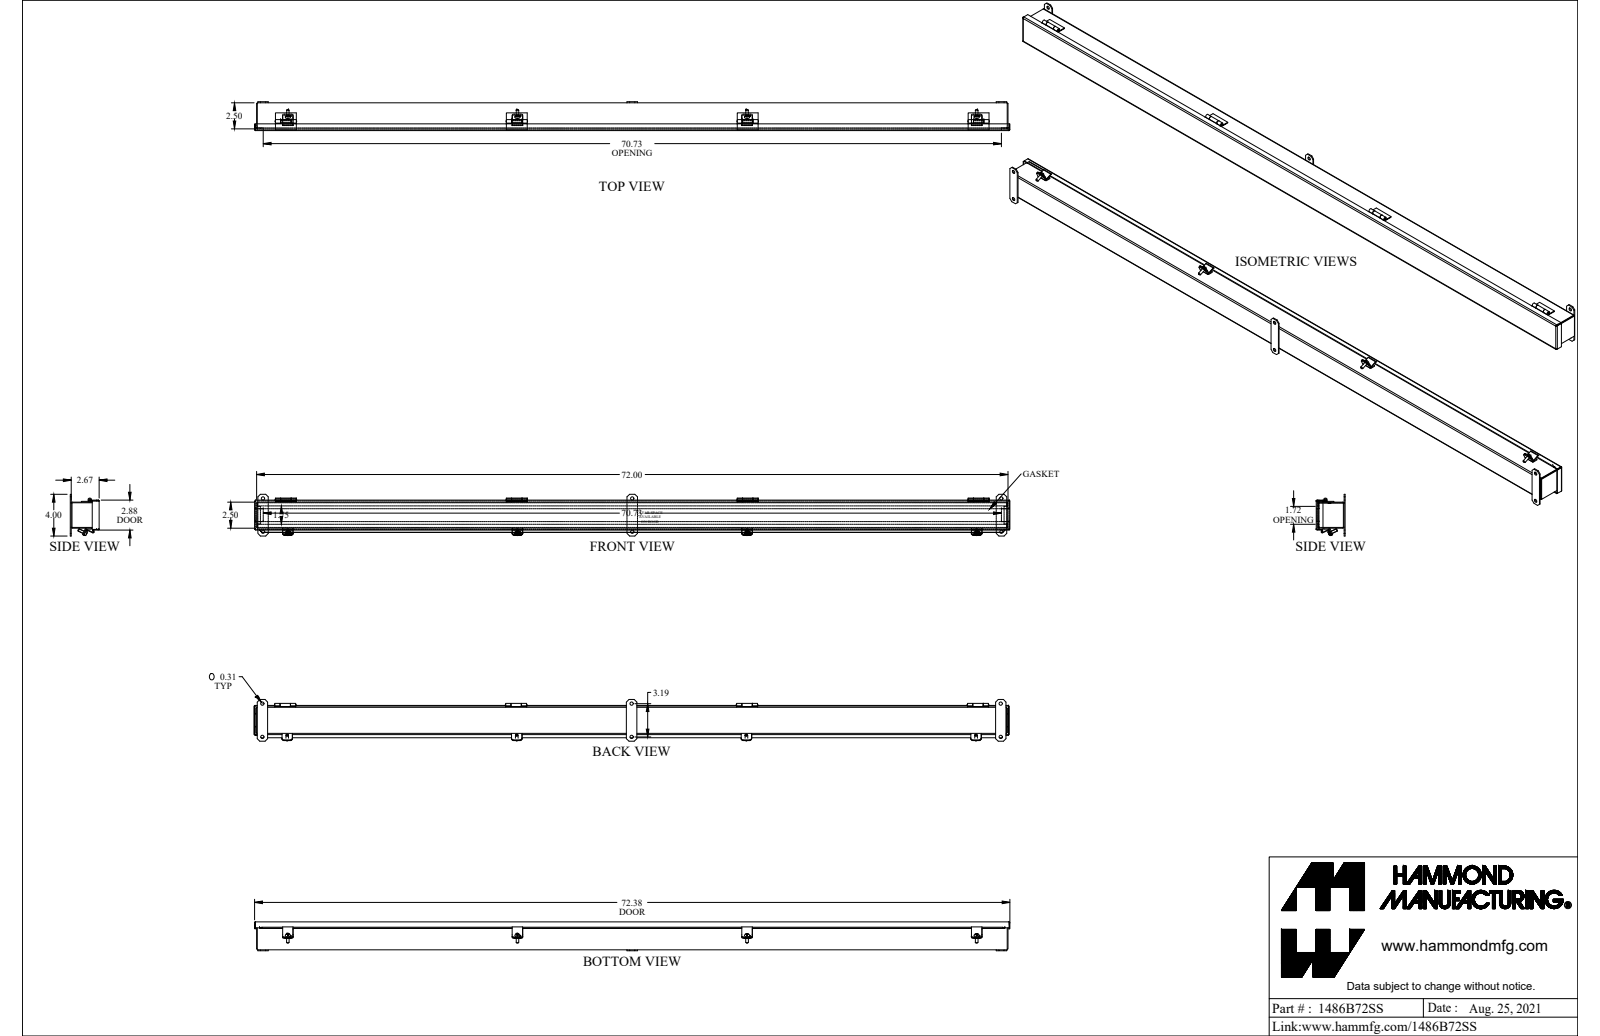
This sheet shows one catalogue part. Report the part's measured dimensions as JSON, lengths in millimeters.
{"part_name": "1486B72SS", "step_written_by": "SolidWorks 2021 (AUTOMOTIVE_DESIGN)", "units": "millimeters", "bodies": {"solids": 16, "faces": 642, "planar": 444, "cylindrical": 160, "other": 38}, "overall_size": [1838.3, 101.6, 70.3], "volume_mm3": 1431000, "surface_area_mm2": 1363000, "round_holes": [[8, 6], [5.4, 4], [4.7, 1]], "round_bosses_or_shafts": [[12.3, 4], [6.4, 4], [8.6, 1], [4.6, 1]], "partial_cylinders_radius": [[4.8, 16], [0.9, 11], [2.7, 11], [0.3, 8], [0.8, 8], [3.6, 8], [0.7, 2], [2.2, 2]], "face_to_face_distances": [1.8, 61.7, 66, 4.7, 59.8, 63.5, 6.6, 64.2, 67.9, 66.4], "hole_center_spacings": [81, 558.8, 898.5, 902.2, 1117.6, 898.5, 902.2, 1676.4]}
